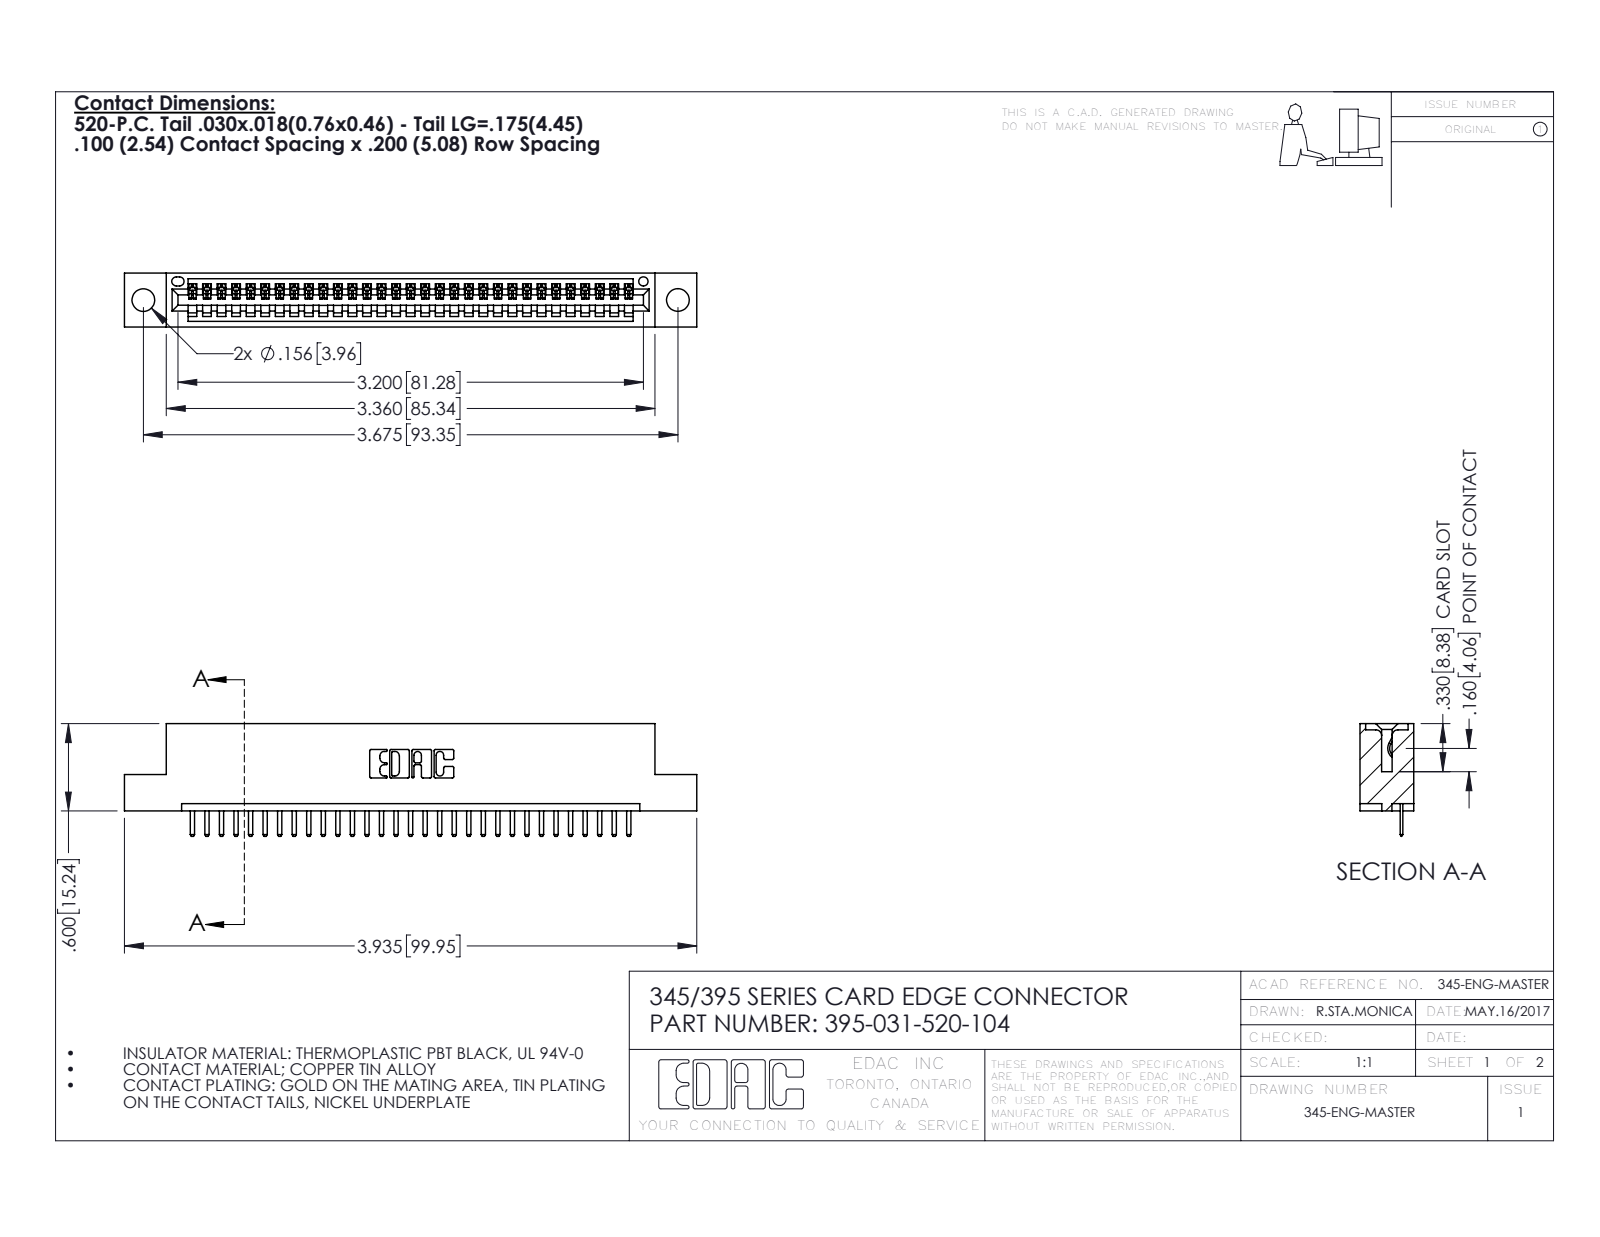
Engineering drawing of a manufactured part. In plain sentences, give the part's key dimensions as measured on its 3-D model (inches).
The part is named "345 Part_Flush Mounting Lugs - 0.156 Dia-TH; 395-031-520-104; 345-292-001_345-293-120". Its 3-D file was written by "SolidWorks 2016 (CONFIG_CONTROL_DESIGN)". It is 32 solids with 2048 faces: 1382 planar, 666 cylindrical and 0 other. Overall it measures 3.935 by 0.775 by 0.37 inches. Its volume is 0.563 cubic inches and its surface area 18.02 square inches. Round holes: 2 of diameter 0.156, 1 of diameter 0.064. Partial cylindrical surfaces (rounded edges, fillets, slot ends): 64 of radius 0.01, 62 of radius 0.006, 22 of radius 0.01, 6 of radius 0.007, 6 of radius 0.031, 3 of radius 0.026, 2 of radius 0.031, 2 of radius 0.04. The main face-to-face distances are 0.298, 0.072, 0.37, 0.2, 0.098, 0.272, 0.025, 0.225, 0.072, 0.149. The hole center spacings are 0.27, 3.44, 3.675.
